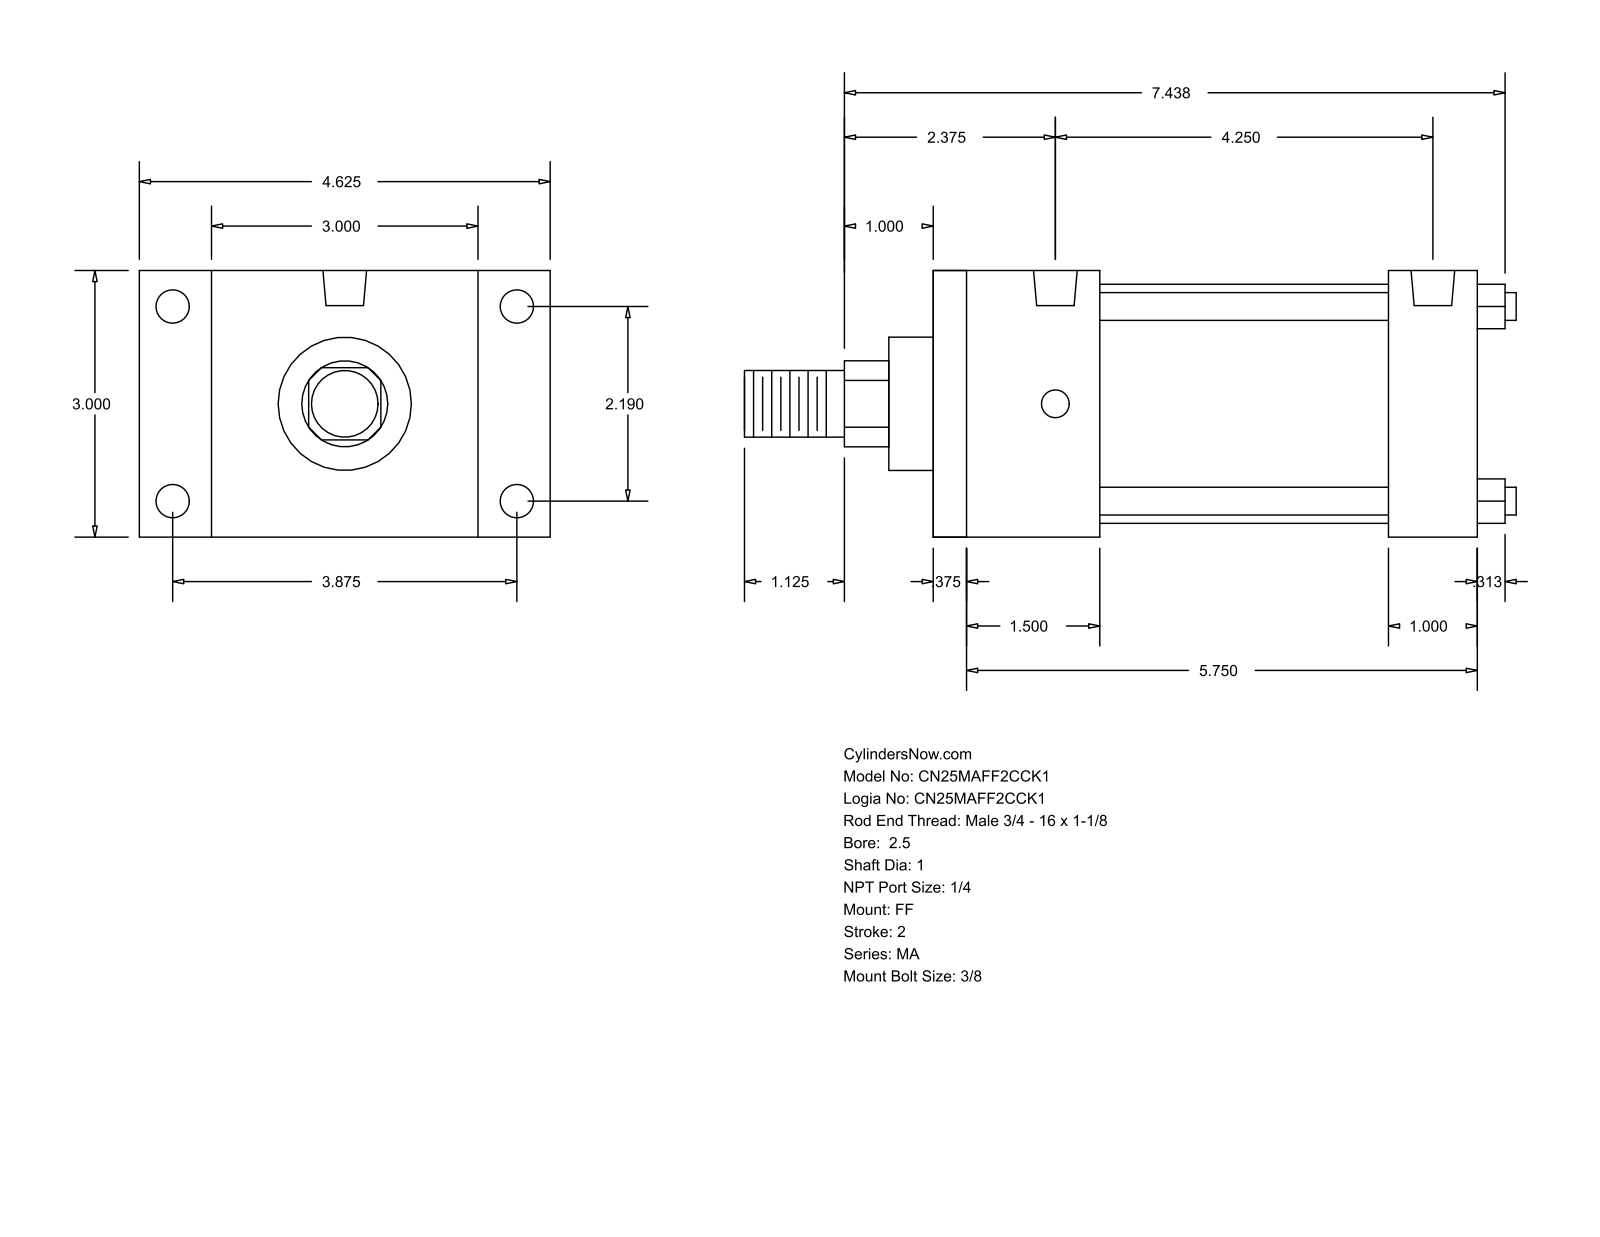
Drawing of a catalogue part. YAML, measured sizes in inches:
part_name: "MA_FF__0250_1"
step_written_by: "GSSL Pune (CONFIG_CONTROL_DESIGN)"
units: inches
bodies: {solids: 0, faces: 92, planar: 64, cylindrical: 28, other: 0}
overall_size: [8.687, 4.625, 3]
round_holes:
  - {diameter: 0.313, count: 4}
  - {diameter: 0.375, count: 4}
  - {diameter: 0.492, count: 2}
round_bosses_or_shafts:
  - {diameter: 0.313, count: 4}
  - {diameter: 2.69, count: 1}
  - {diameter: 1.5, count: 1}
  - {diameter: 1, count: 1}
  - {diameter: 0.75, count: 1}
partial_cylinders:
  - {radius: 0.484, count: 1}
face_to_face_distances: [3, 6.125, 0.375, 5.75, 1, 1.875, 5.125, 1.5, 4.75, 3.25]
hole_center_spacings: [2.19, 3.875, 4.25, 4.451]
